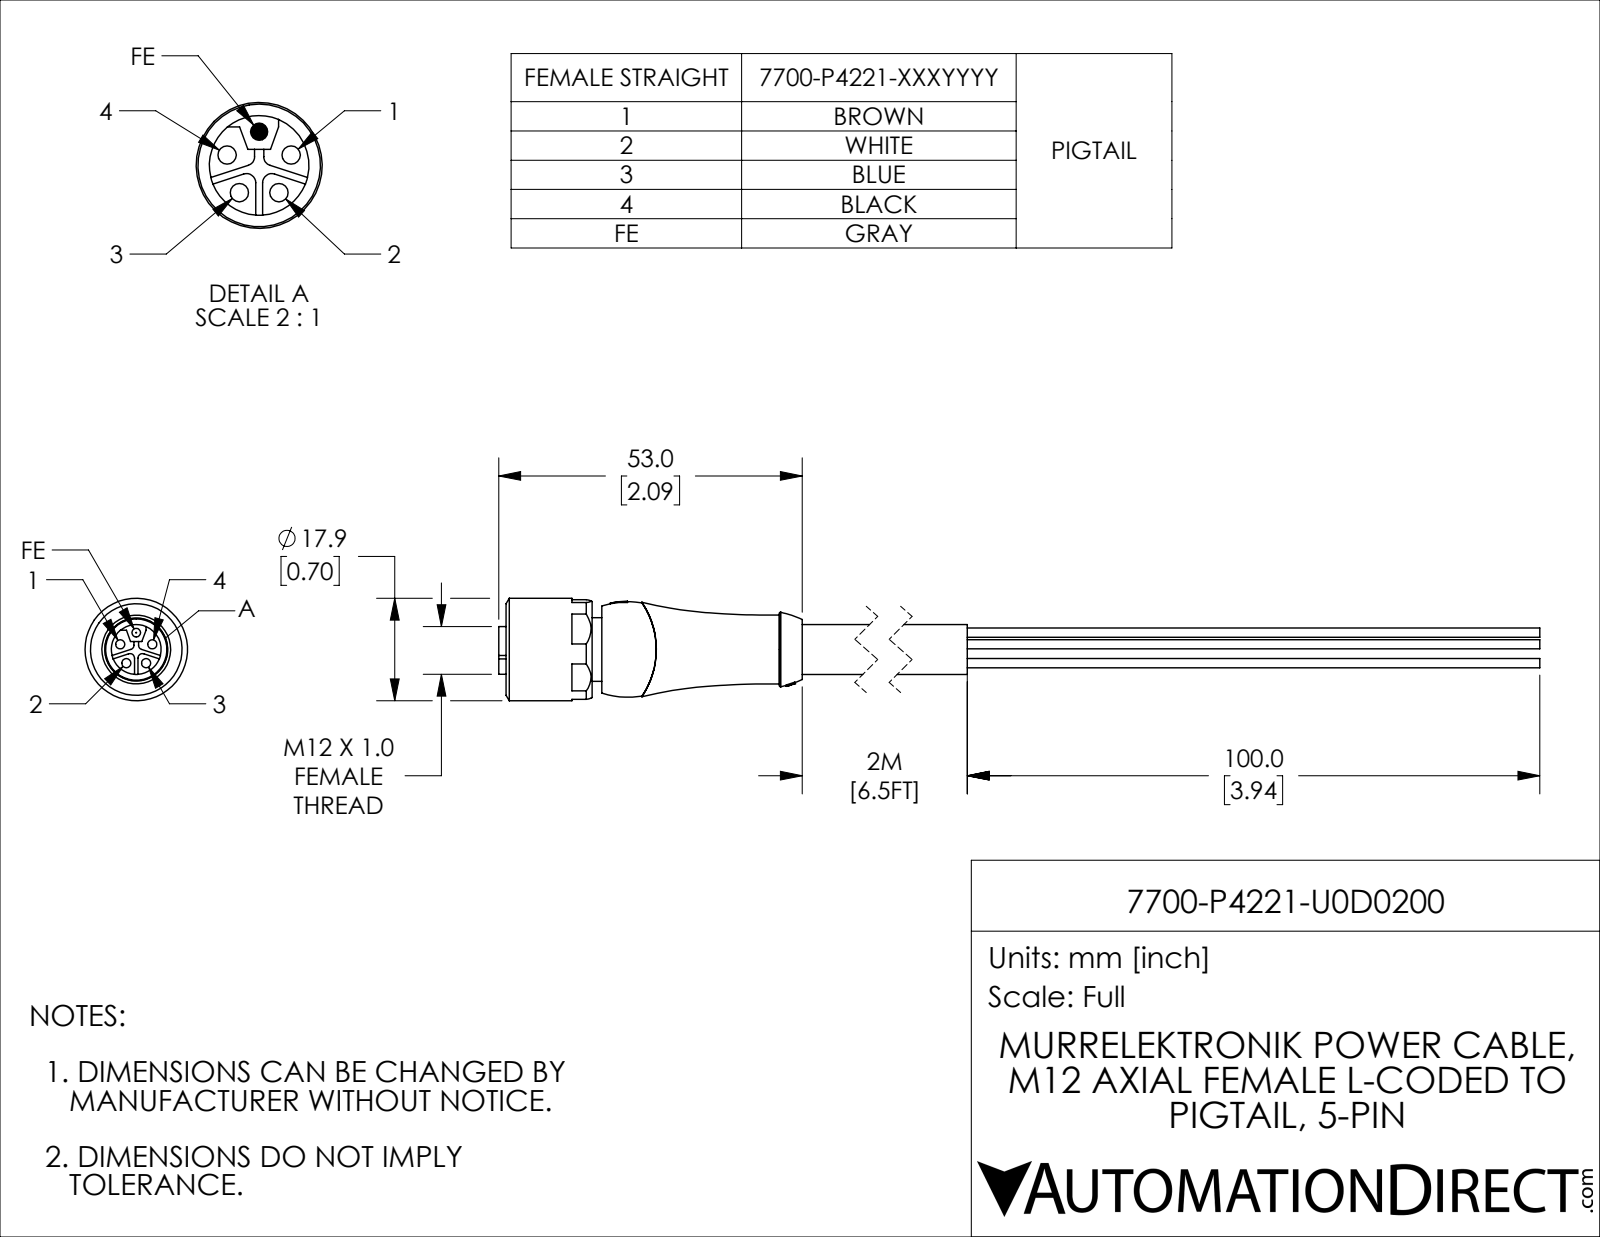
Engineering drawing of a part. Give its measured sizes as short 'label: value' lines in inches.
name: 7700-P4221-U0D0200
written by: SolidWorks 2021 (CONFIG_CONTROL_DESIGN)
unit: in
bodies: 2 solids, 142 faces (69 planar, 40 cylindrical, 33 other)
size: 7.598 × 0.705 × 0.705
volume: 0.735 in³; area: 12.83 in²
holes: 4× ⌀0.063, 1× ⌀0.433, 1× ⌀0.512
bosses: 1× ⌀0.705, 1× ⌀0.51, 1× ⌀0.437, 1× ⌀0.343, 1× ⌀0.063, 1× ⌀0.059
rounds: 4× R0.031
face distances: 0.657, 0.591, 0.067, 0.667, 3.61, 3.02, 2.953, 0.181, 0.362, 0.228
hole spacings: 0.116, 0.136, 0.22
